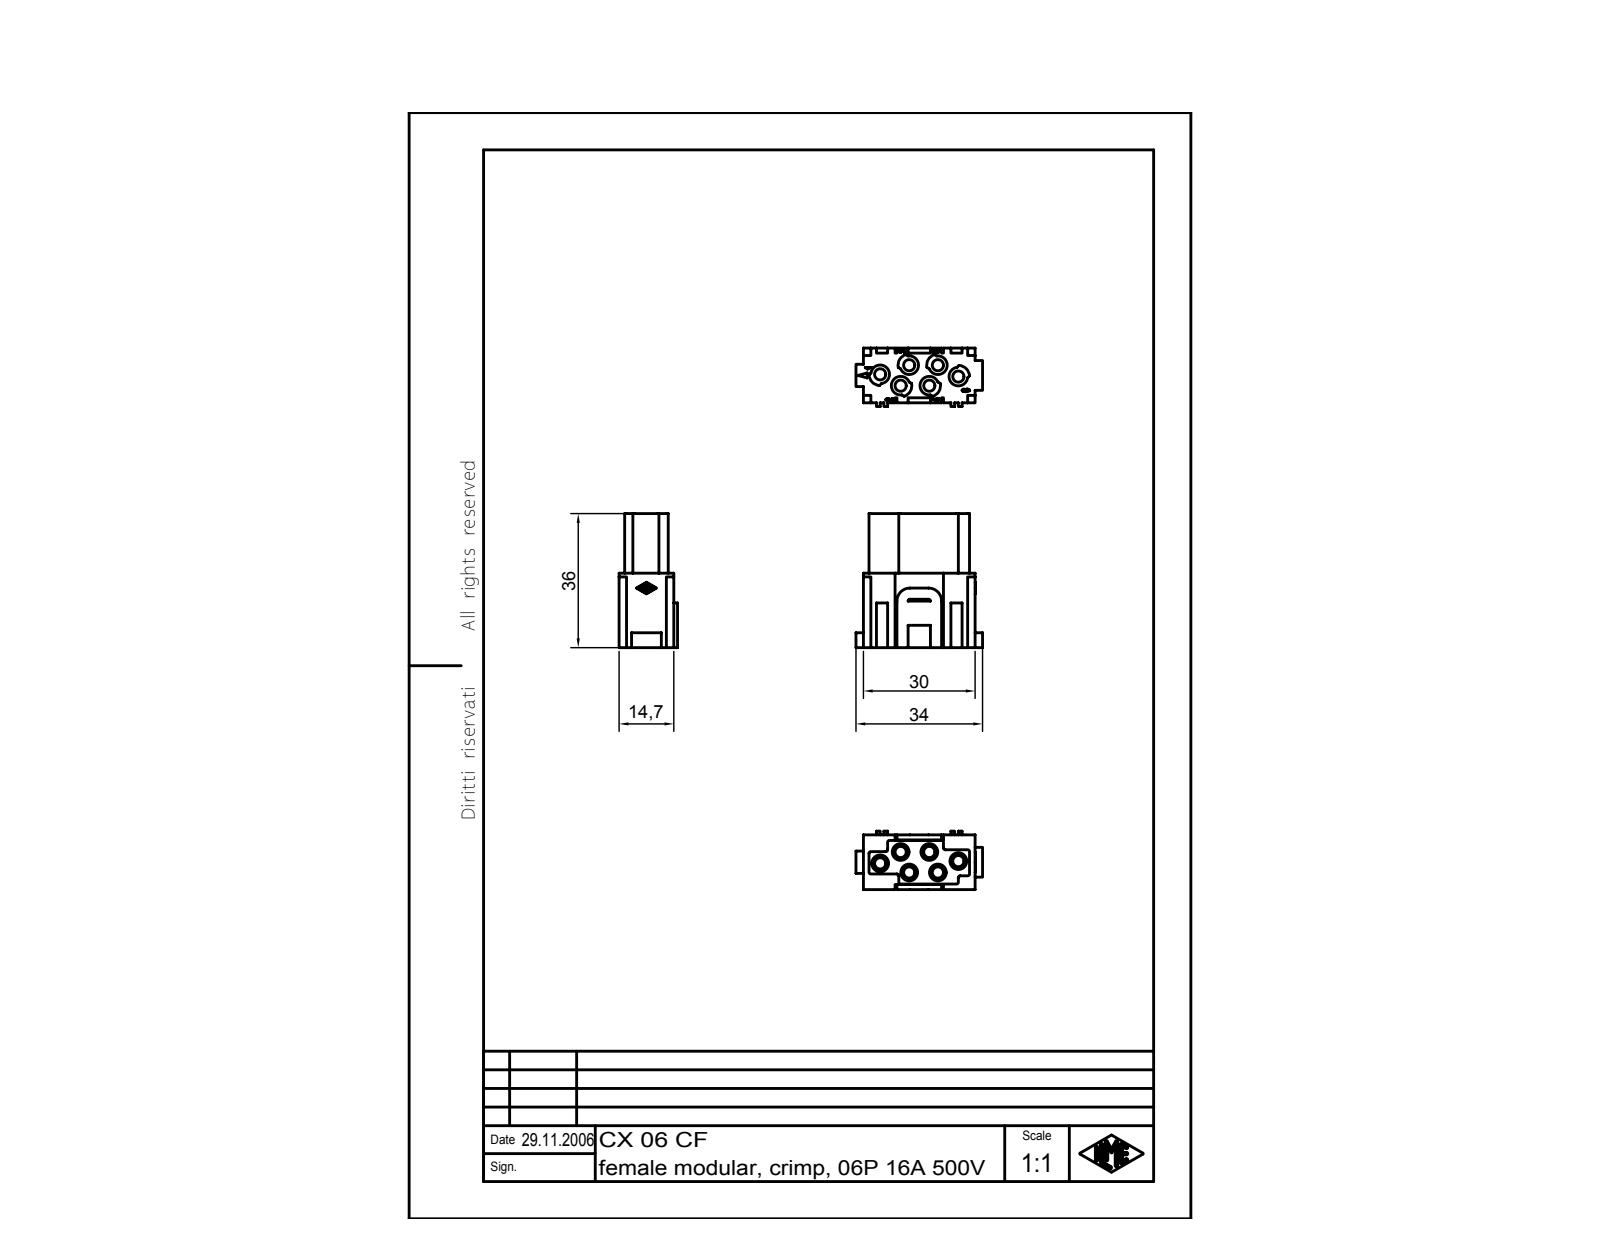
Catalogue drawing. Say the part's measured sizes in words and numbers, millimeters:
The part is named "CX 06 CF". Its 3-D file was written by "Autodesk Inventor 7 (AUTOMOTIVE_DESIGN)". It is 1 solid with 325 faces: 175 planar, 48 cylindrical and 102 other. Overall it measures 36 by 34 by 15.7 millimeters. Its volume is 9 018 cubic millimeters and its surface area 7 250 square millimeters. Partial cylindrical surfaces (rounded edges, fillets, slot ends): 14 of radius 0.1, 14 of radius 0.5, 6 of radius 2.5, 6 of radius 3, 2 of radius 3.5. The main face-to-face distances are 1.5, 2, 13.2, 14.7, 4, 6.5, 20, 0.5, 3, 18.
